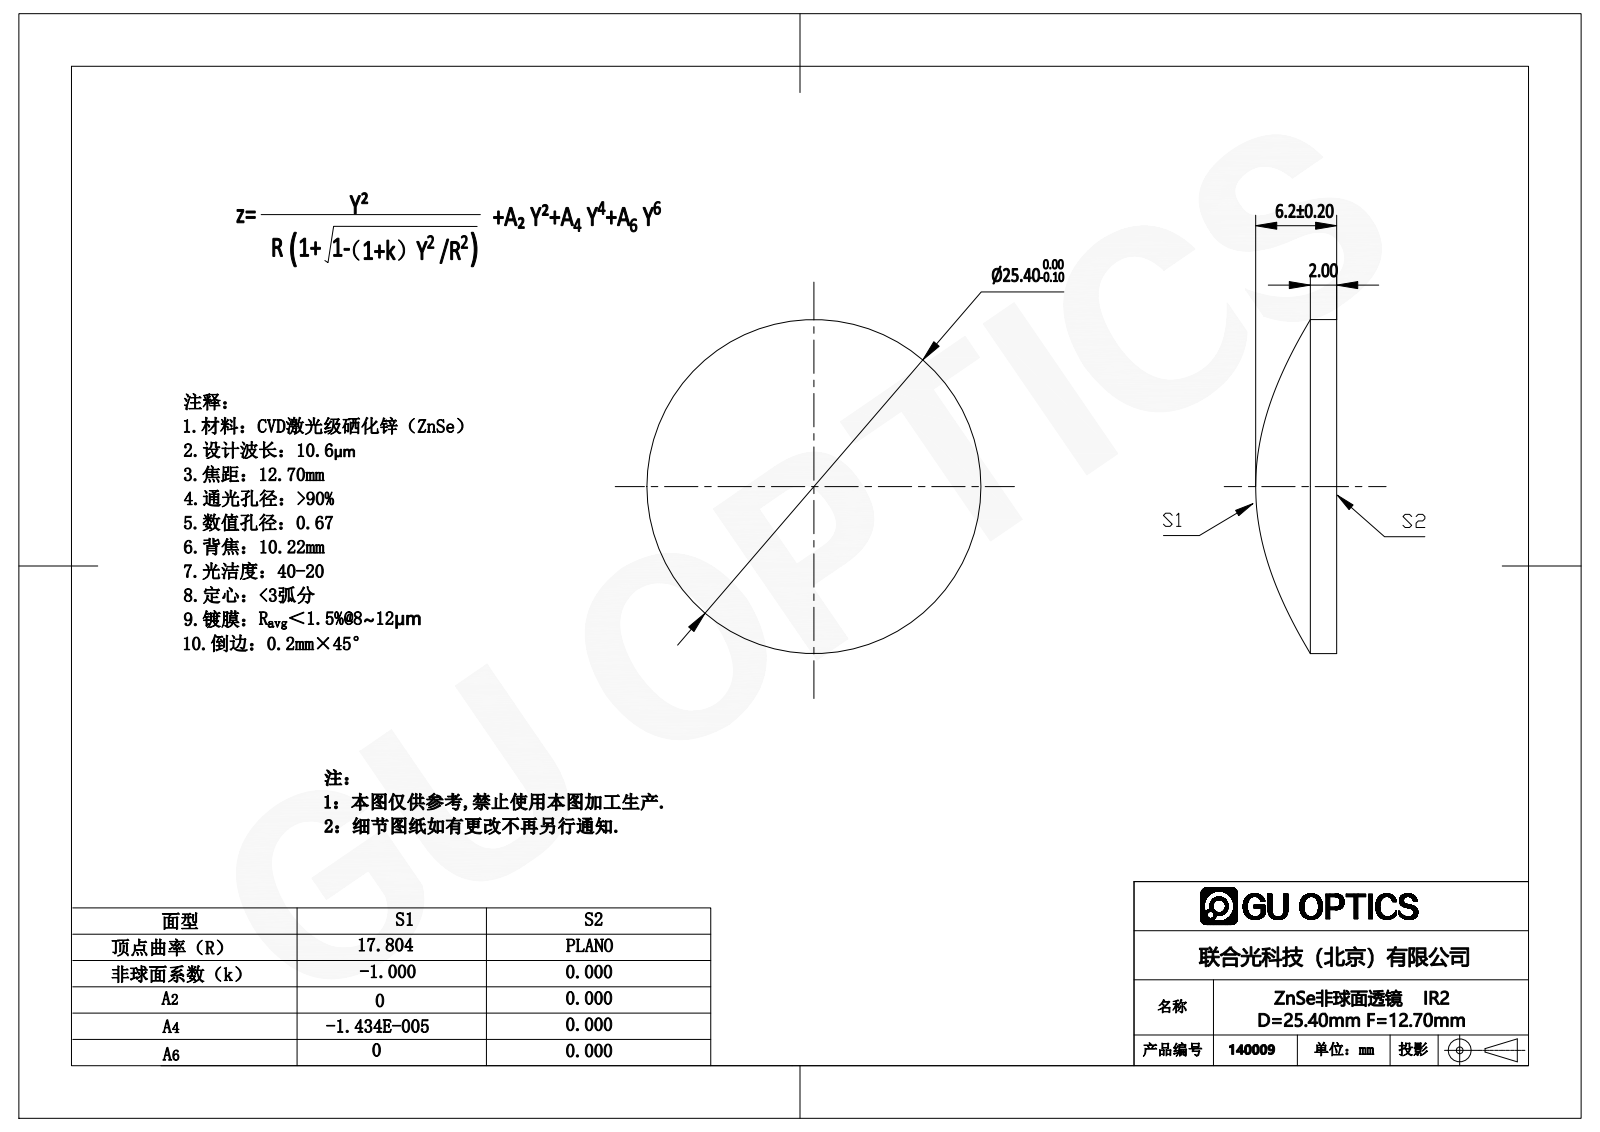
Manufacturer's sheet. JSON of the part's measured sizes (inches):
{"part_name": "140009", "step_written_by": "SolidWorks 2020 (CONFIG_CONTROL_DESIGN)", "units": "inches", "bodies": {"solids": 1, "faces": 5, "planar": 1, "cylindrical": 2, "other": 2}, "overall_size": [1, 1, 0.243], "volume_in3": 0.124, "surface_area_in2": 1.894, "round_bosses_or_shafts": [[1, 1]]}
